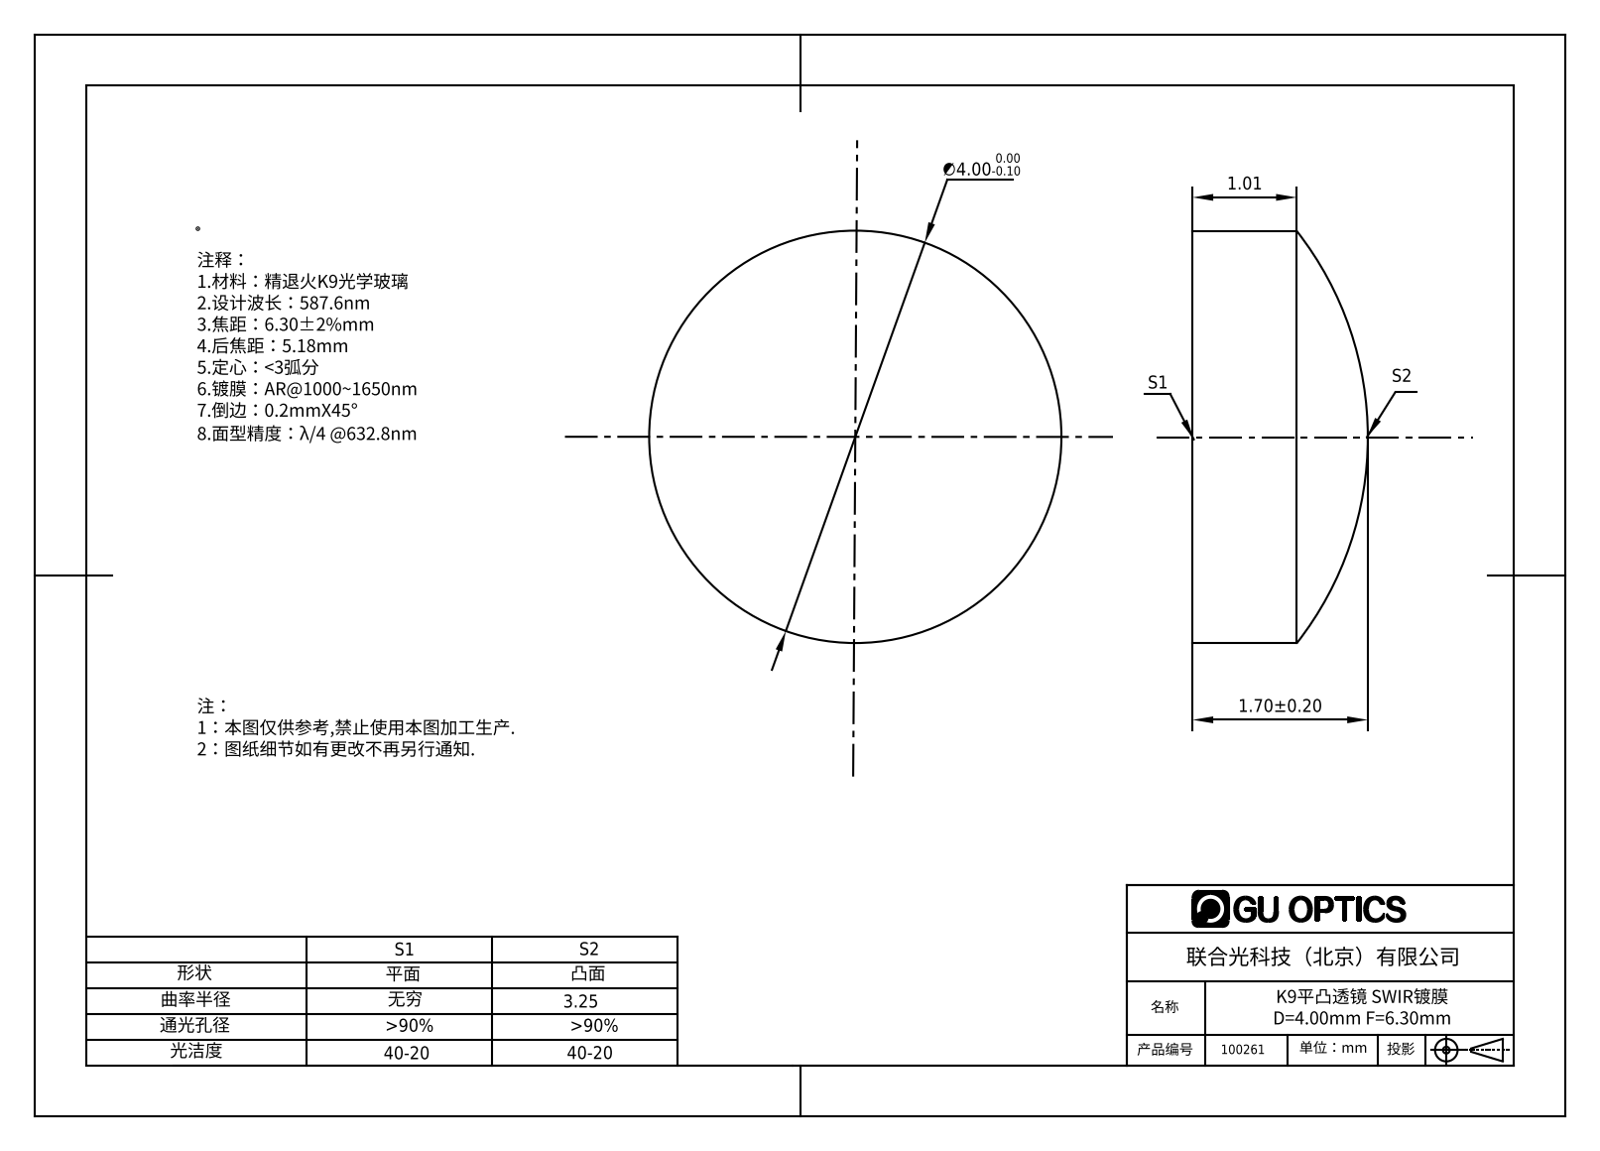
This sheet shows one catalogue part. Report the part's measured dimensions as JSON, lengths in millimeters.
{"part_name": "100089", "step_written_by": "SolidWorks 2016 (AUTOMOTIVE_DESIGN)", "units": "millimeters", "bodies": {"solids": 1, "faces": 5, "planar": 1, "cylindrical": 2, "other": 2}, "overall_size": [4, 4, 1.7], "volume_mm3": 17, "surface_area_mm2": 39, "round_bosses_or_shafts": [[4, 1]]}
